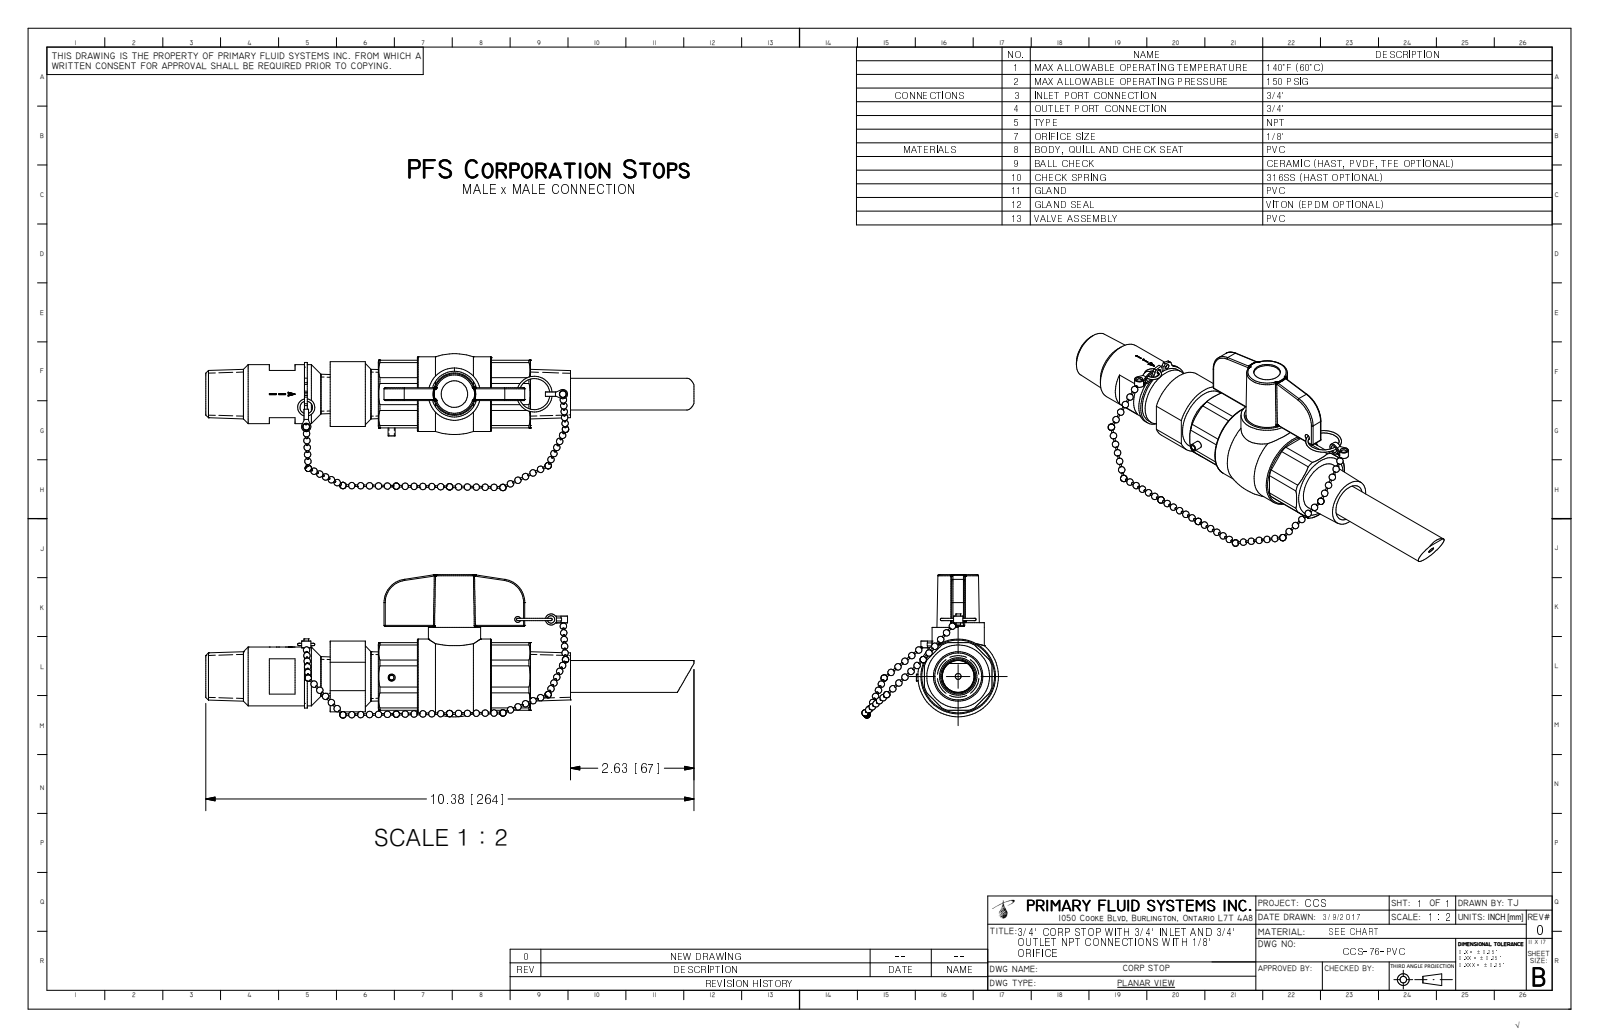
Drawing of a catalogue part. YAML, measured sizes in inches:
part_name: "CCS-76-PVC_R0"
step_written_by: "Autodesk Inventor 2009 (AUTOMOTIVE_DESIGN)"
units: inches
bodies: {solids: 1, faces: 382, planar: 113, cylindrical: 62, other: 207}
overall_size: [10.38, 3.043, 2.905]
volume: 12.99
surface_area: 67.52
round_holes:
  - {diameter: 0.098, count: 1}
  - {diameter: 0.125, count: 1}
  - {diameter: 0.15, count: 1}
  - {diameter: 0.25, count: 1}
  - {diameter: 0.469, count: 1}
  - {diameter: 0.56, count: 1}
  - {diameter: 0.563, count: 1}
  - {diameter: 0.97, count: 1}
round_bosses_or_shafts:
  - {diameter: 1.585, count: 1}
  - {diameter: 1.343, count: 1}
  - {diameter: 1.25, count: 1}
  - {diameter: 1.14, count: 1}
  - {diameter: 1.11, count: 1}
  - {diameter: 0.9, count: 1}
  - {diameter: 0.675, count: 1}
  - {diameter: 0.558, count: 1}
partial_cylinders:
  - {radius: 0.025, count: 12}
  - {radius: 0.054, count: 2}
  - {radius: 0.197, count: 2}
  - {radius: 0.5, count: 2}
  - {radius: 0.451, count: 1}
  - {radius: 0.563, count: 1}
  - {radius: 0.624, count: 1}
  - {radius: 0.75, count: 1}
face_to_face_distances: [1.435, 0.55, 0.03, 0.275, 0.825, 0.187, 1.187, 0.363, 0.637, 0.217]
hole_center_spacings: [0.69]
